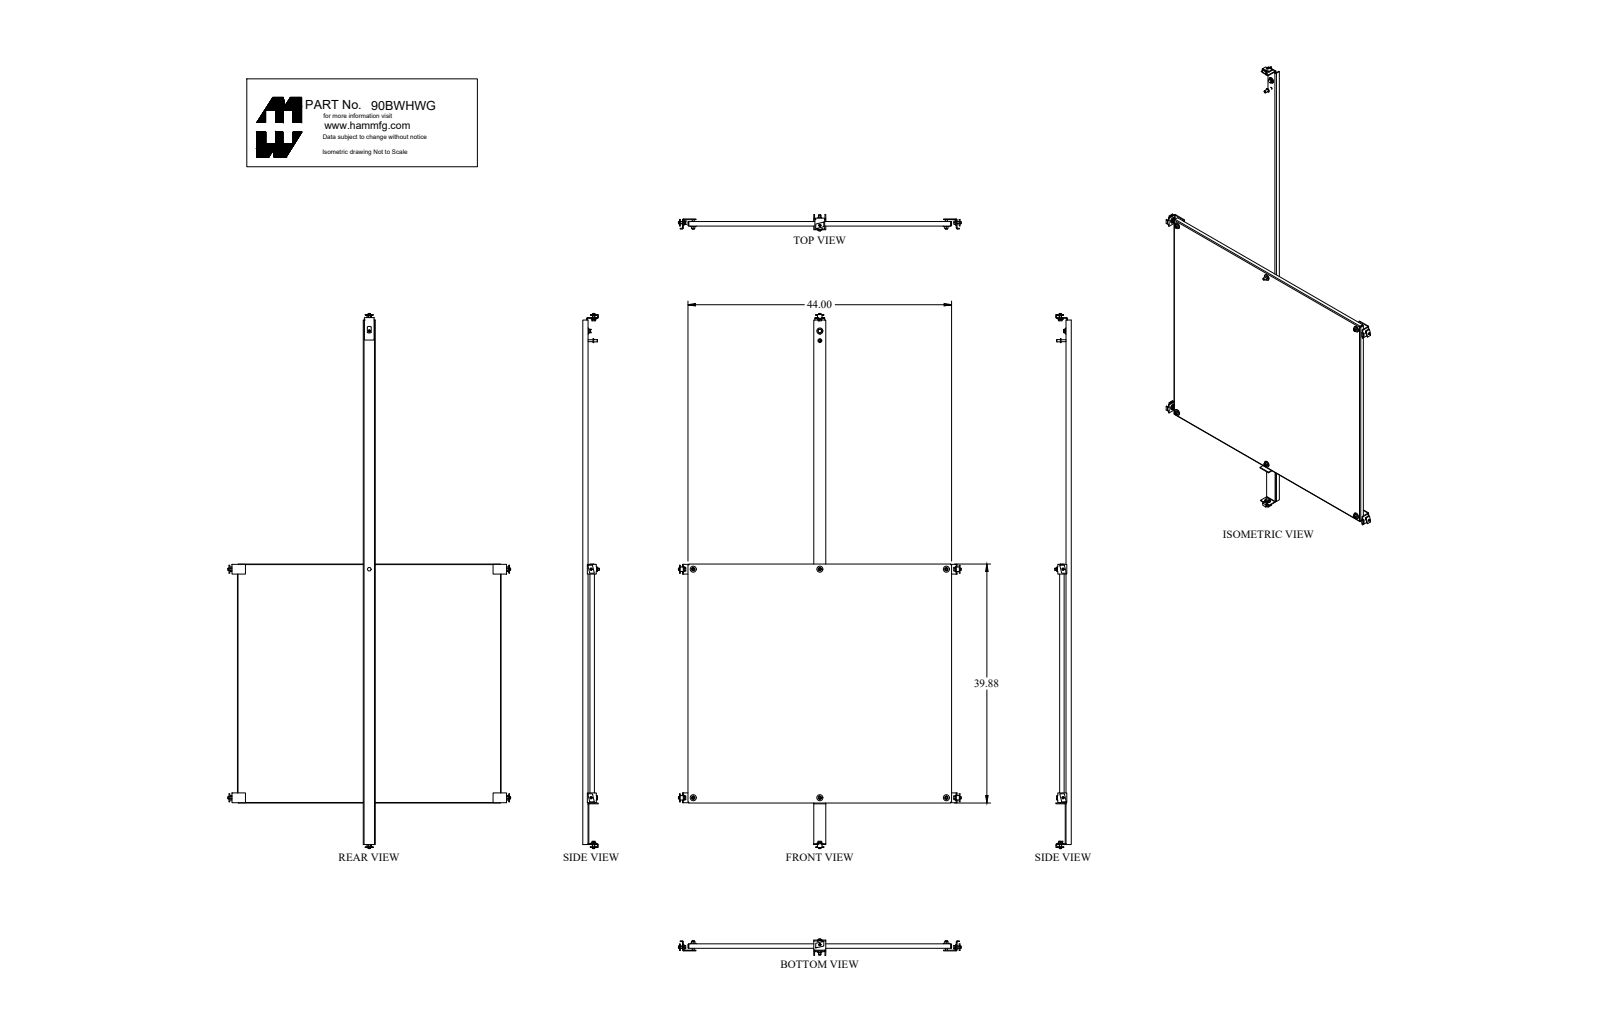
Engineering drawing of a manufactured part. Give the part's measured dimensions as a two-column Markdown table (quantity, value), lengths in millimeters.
| quantity | value |
| --- | --- |
| part name | 90BWHWG_Default |
| STEP written by | SolidWorks 2018 (CONFIG_CONTROL_DESIGN) |
| units | millimeters |
| bodies | 14 solids, 305 faces (152 planar, 105 cylindrical, 48 other) |
| overall size | 2258.2 × 1183.2 × 65.9 |
| volume | 3 622 000 mm³ |
| surface area | 2 888 000 mm² |
| round holes (diameter × count) | 14.3 × 6, 11.1 × 5, 11.1 × 1, 11.5 × 1 |
| round bosses / shafts (diameter × count) | 16.5 × 6, 8.4 × 6, 9.5 × 4, 9.5 × 2 |
| partial cylindrical surfaces (radius × count) | 1.5 × 11, 4.7 × 11, 1.2 × 4, 3.6 × 4, 5.6 × 2 |
| main face-to-face distances | 2.4, 3.2, 30.1, 27, 24.6, 27.7, 3.2, 50.8, 47.6, 44.5 |
| hole center spacings | 1107.1, 968.4, 536.6, 536.6, 1073.2, 1445.5, 2049.1, 0.8 |
